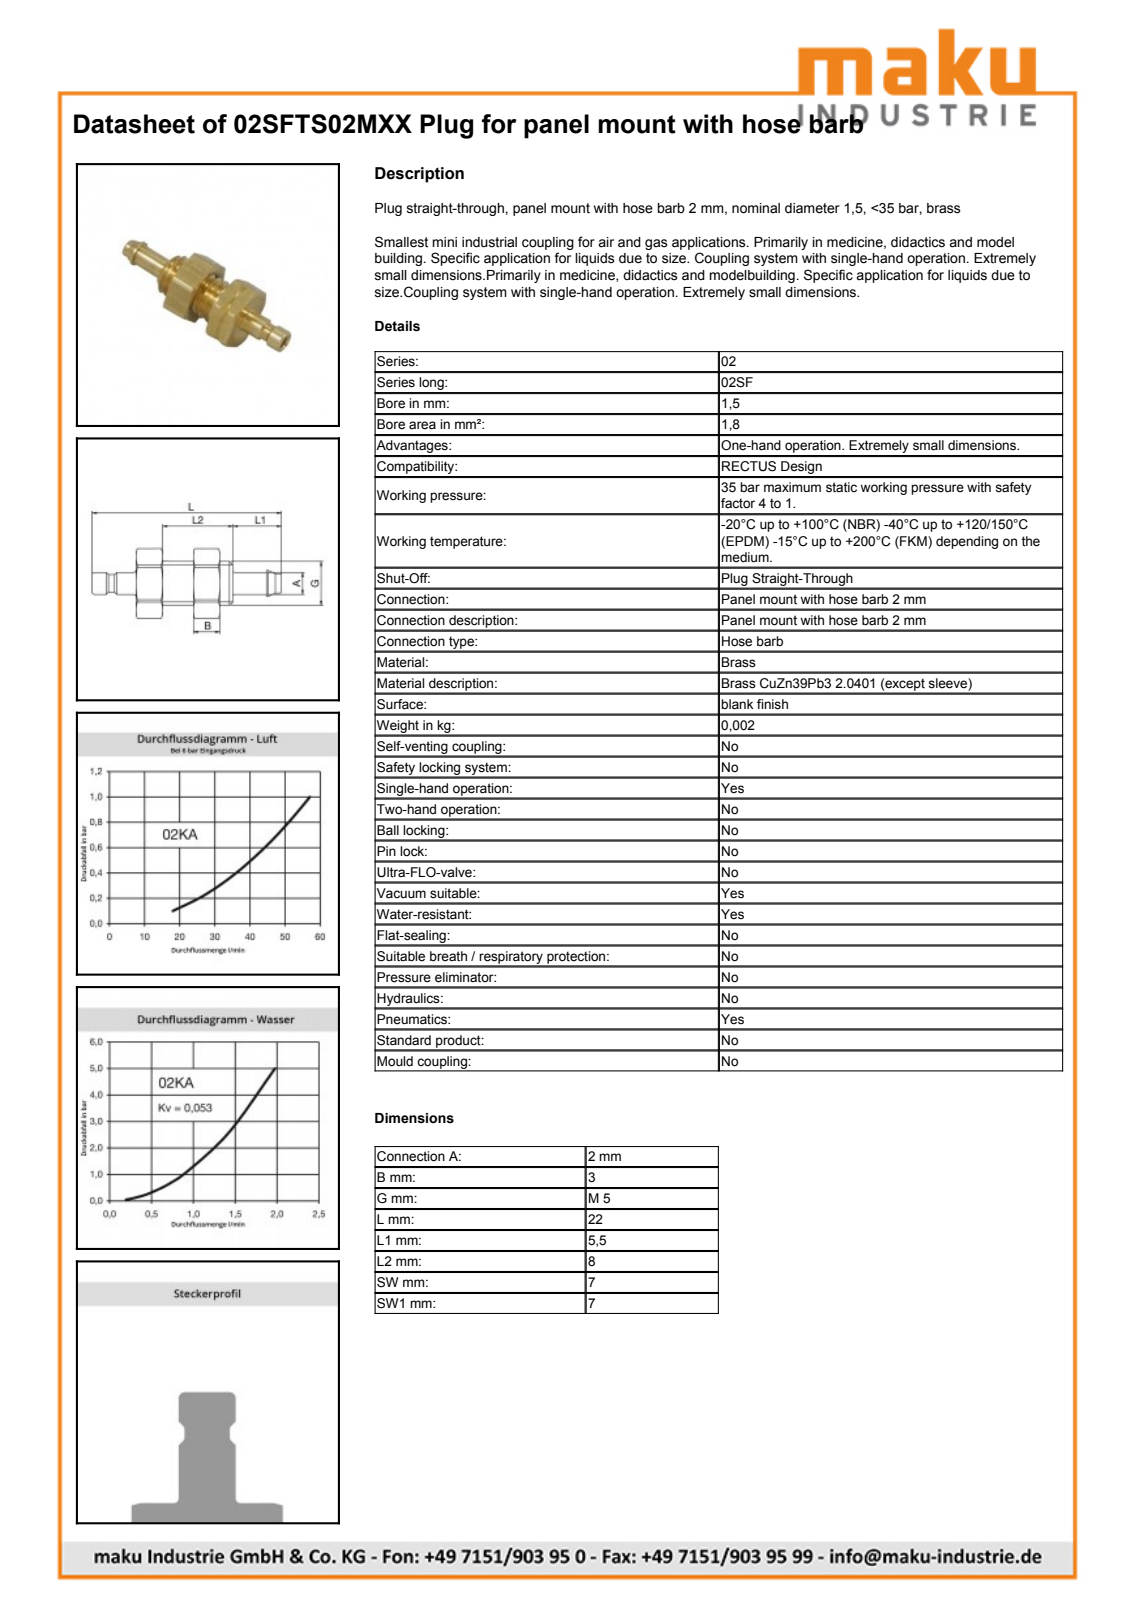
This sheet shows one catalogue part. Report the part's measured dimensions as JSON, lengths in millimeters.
{"part_name": "D104491; D104455; D104452", "step_written_by": "Autodesk Inventor 2011 (AUTOMOTIVE_DESIGN)", "units": "millimeters", "bodies": {"solids": 2, "faces": 91, "planar": 26, "cylindrical": 27, "other": 38}, "overall_size": [21.5, 7.9, 7.8], "volume_mm3": 368, "surface_area_mm2": 618, "round_holes": [[1.5, 1], [4.48, 1]], "round_bosses_or_shafts": [[5, 1], [2.95, 1], [2.54, 1], [2.5, 1], [2.2, 1], [2, 1]], "partial_cylinders_radius": [[3.95, 1]], "face_to_face_distances": [7, 3, 5.6, 2.6, 8.6, 8, 11, 5.4, 2.4, 5]}
